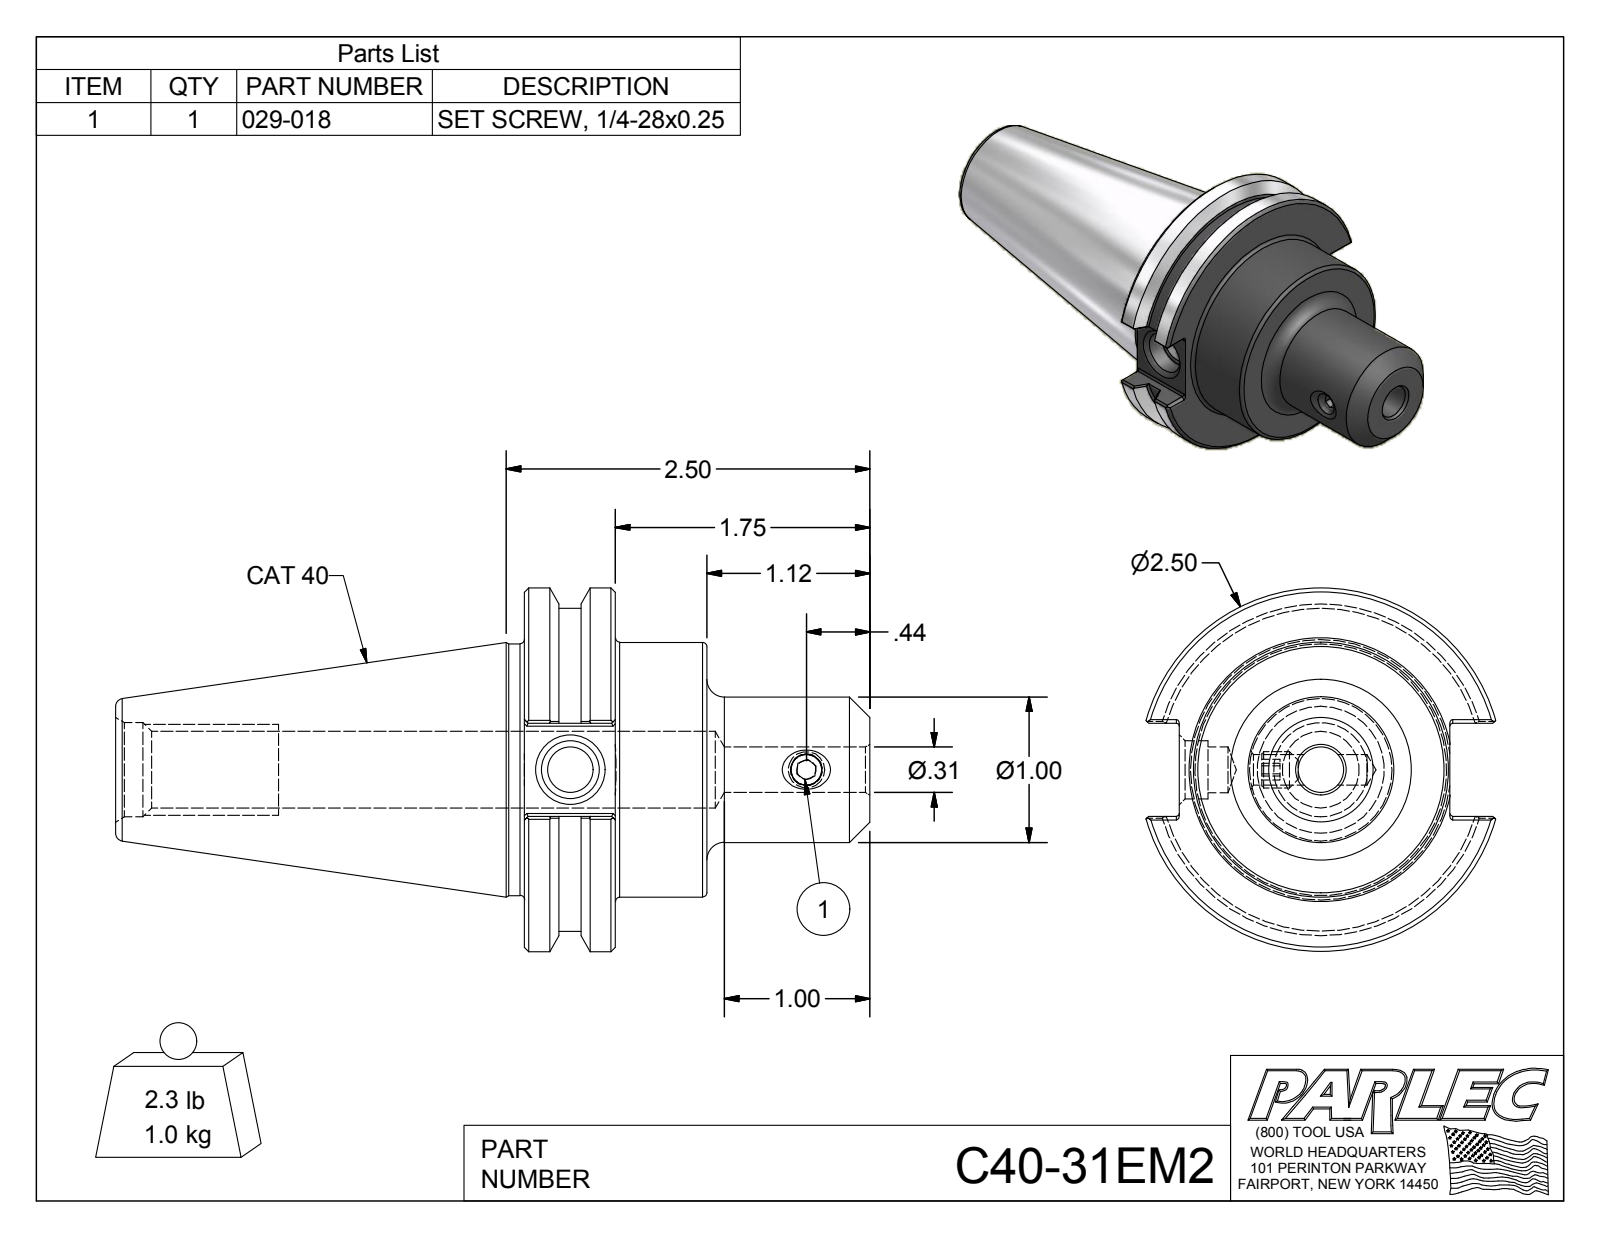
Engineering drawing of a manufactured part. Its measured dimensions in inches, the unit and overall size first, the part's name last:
Units: inches
Overall size (bounding box): 5.188 × 2.5 × 2.417
Round holes (diameter × count): ⌀0.211 ×1, ⌀0.313 ×1, ⌀0.527 ×1, ⌀0.563 ×1, ⌀0.648 ×1
Round bosses / shafts (diameter × count): ⌀2.5 ×1, ⌀2.219 ×1, ⌀1.75 ×1, ⌀1 ×1, ⌀0.25 ×1
Main face-to-face distances: 0.625, 1.255, 0.63, 2.375, 1.75, 1.12, 0.64, 2.813, 3.437, 4.067
Hole centre spacings: 1.622
Volume: 8.279 in³ · Surface area: 40.27 in²
Bodies: 2 solids, 60 faces (20 planar, 15 cylindrical, 25 other)
Part name (STEP PRODUCT): C40-31EM2; C40-31EM2-1; 029-018
STEP written by: Autodesk Inventor 2012 (AUTOMOTIVE_DESIGN)
